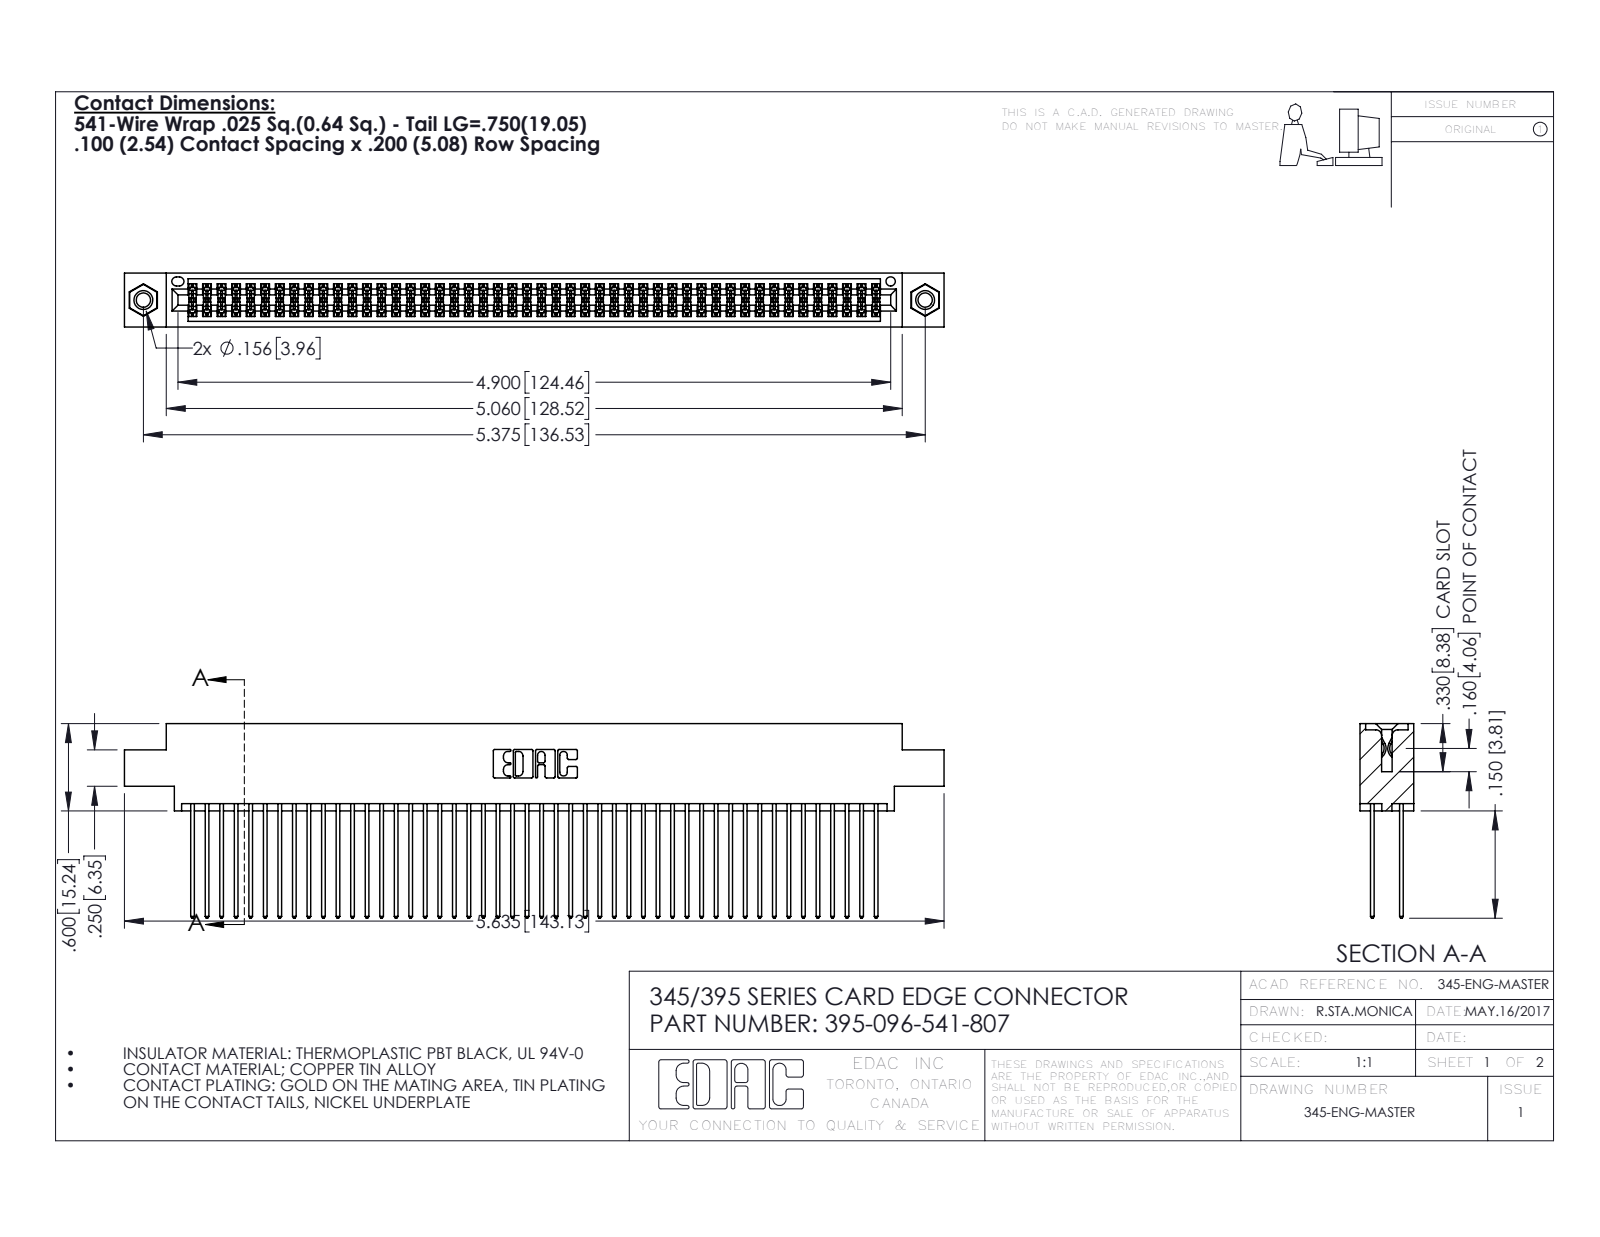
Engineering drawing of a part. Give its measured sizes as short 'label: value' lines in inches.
name: 345 Part_0.170 Offset - 0.156 Dia-TI; 395-096-541-807; 345-292-001_345-293-141; 345-250-001_345-250-005-103
written by: SolidWorks 2016 (CONFIG_CONTROL_DESIGN)
unit: in
bodies: 99 solids, 4990 faces (3284 planar, 1690 cylindrical, 16 other)
size: 5.635 × 1.337 × 0.37
volume: 0.878 in³; area: 37.41 in²
holes: 2× ⌀0.098, 2× ⌀0.125, 2× ⌀0.156, 1× ⌀0.064
bosses: 2× ⌀0.155
rounds: 144× R0.006, 96× R0.01, 22× R0.01, 6× R0.007, 6× R0.031, 3× R0.026, 2× R0.014, 2× R0.019
face distances: 0.072, 0.298, 0.2, 0.098, 0.272, 0.025, 0.225, 0.37, 0.175, 0.149
hole spacings: 0.27, 5.139, 5.375
